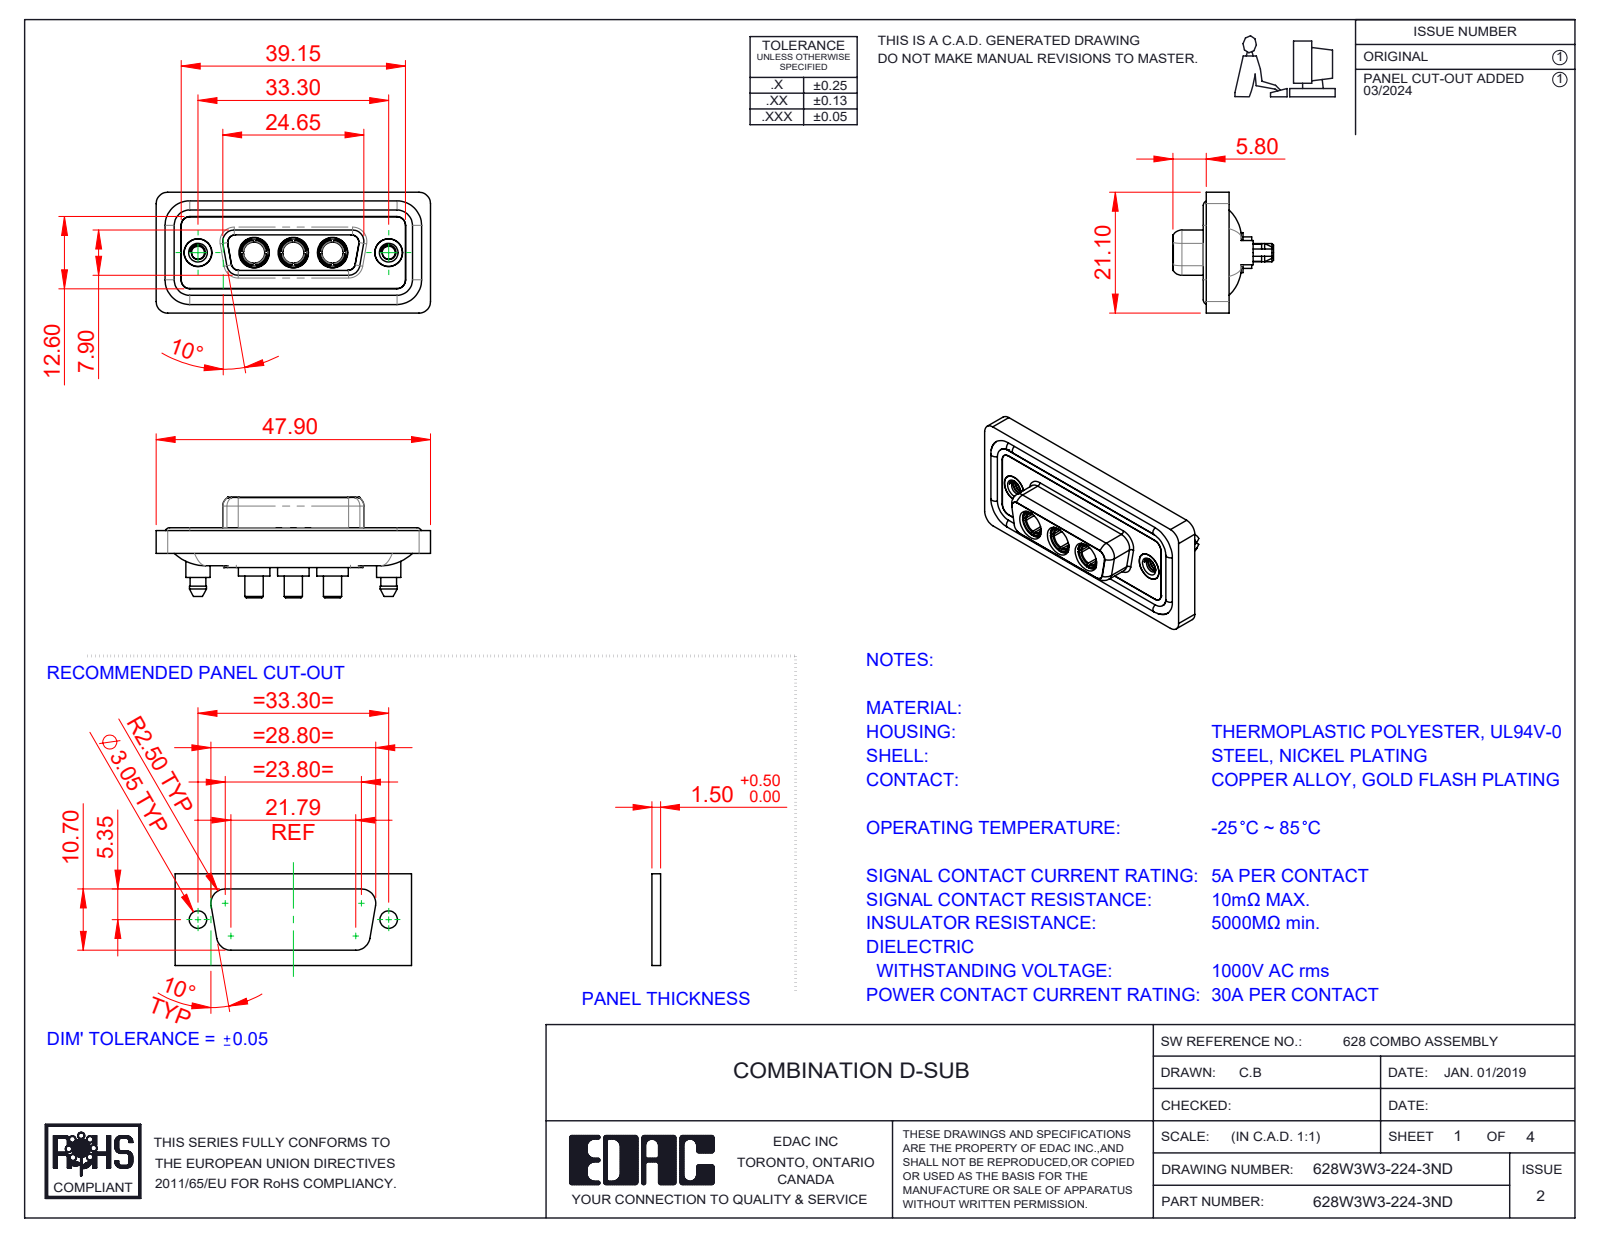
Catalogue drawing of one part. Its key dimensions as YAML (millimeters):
part_name: "628Combo Threaded Boardlock_D; Power Socket_30A S; 628W3W3-224-3ND; 628Combo Shell Rear_15 Contacts (+3 more)"
step_written_by: "SolidWorks 2023 (CONFIG_CONTROL_DESIGN)"
units: millimeters
bodies: {solids: 13, faces: 674, planar: 208, cylindrical: 305, other: 161}
overall_size: [47.9, 21.1, 17.55]
volume: 6183
surface_area: 10092
round_holes:
  - {diameter: 4.85, count: 5}
  - {diameter: 3.7, count: 3}
  - {diameter: 5.3, count: 3}
  - {diameter: 2.26, count: 2}
  - {diameter: 4, count: 2}
  - {diameter: 4.05, count: 2}
  - {diameter: 5, count: 2}
round_bosses_or_shafts:
  - {diameter: 1.6, count: 4}
  - {diameter: 5.5, count: 3}
  - {diameter: 5.2, count: 3}
  - {diameter: 4.96, count: 3}
  - {diameter: 4.75, count: 3}
  - {diameter: 3.75, count: 3}
  - {diameter: 3.2, count: 3}
  - {diameter: 5.4, count: 2}
partial_cylinders:
  - {radius: 1.5, count: 24}
  - {radius: 2, count: 20}
  - {radius: 1.35, count: 12}
  - {radius: 1.6, count: 10}
  - {radius: 0.25, count: 4}
  - {radius: 0.5, count: 4}
  - {radius: 0.6, count: 4}
  - {radius: 0.65, count: 4}
face_to_face_distances: [0.4, 1.8, 1.6, 0.5, 7.45, 1.1, 2.9, 5.65, 7.05, 6.6]
hole_center_spacings: [6.85, 9.8, 16.65, 23.5, 13.7, 33.3]
